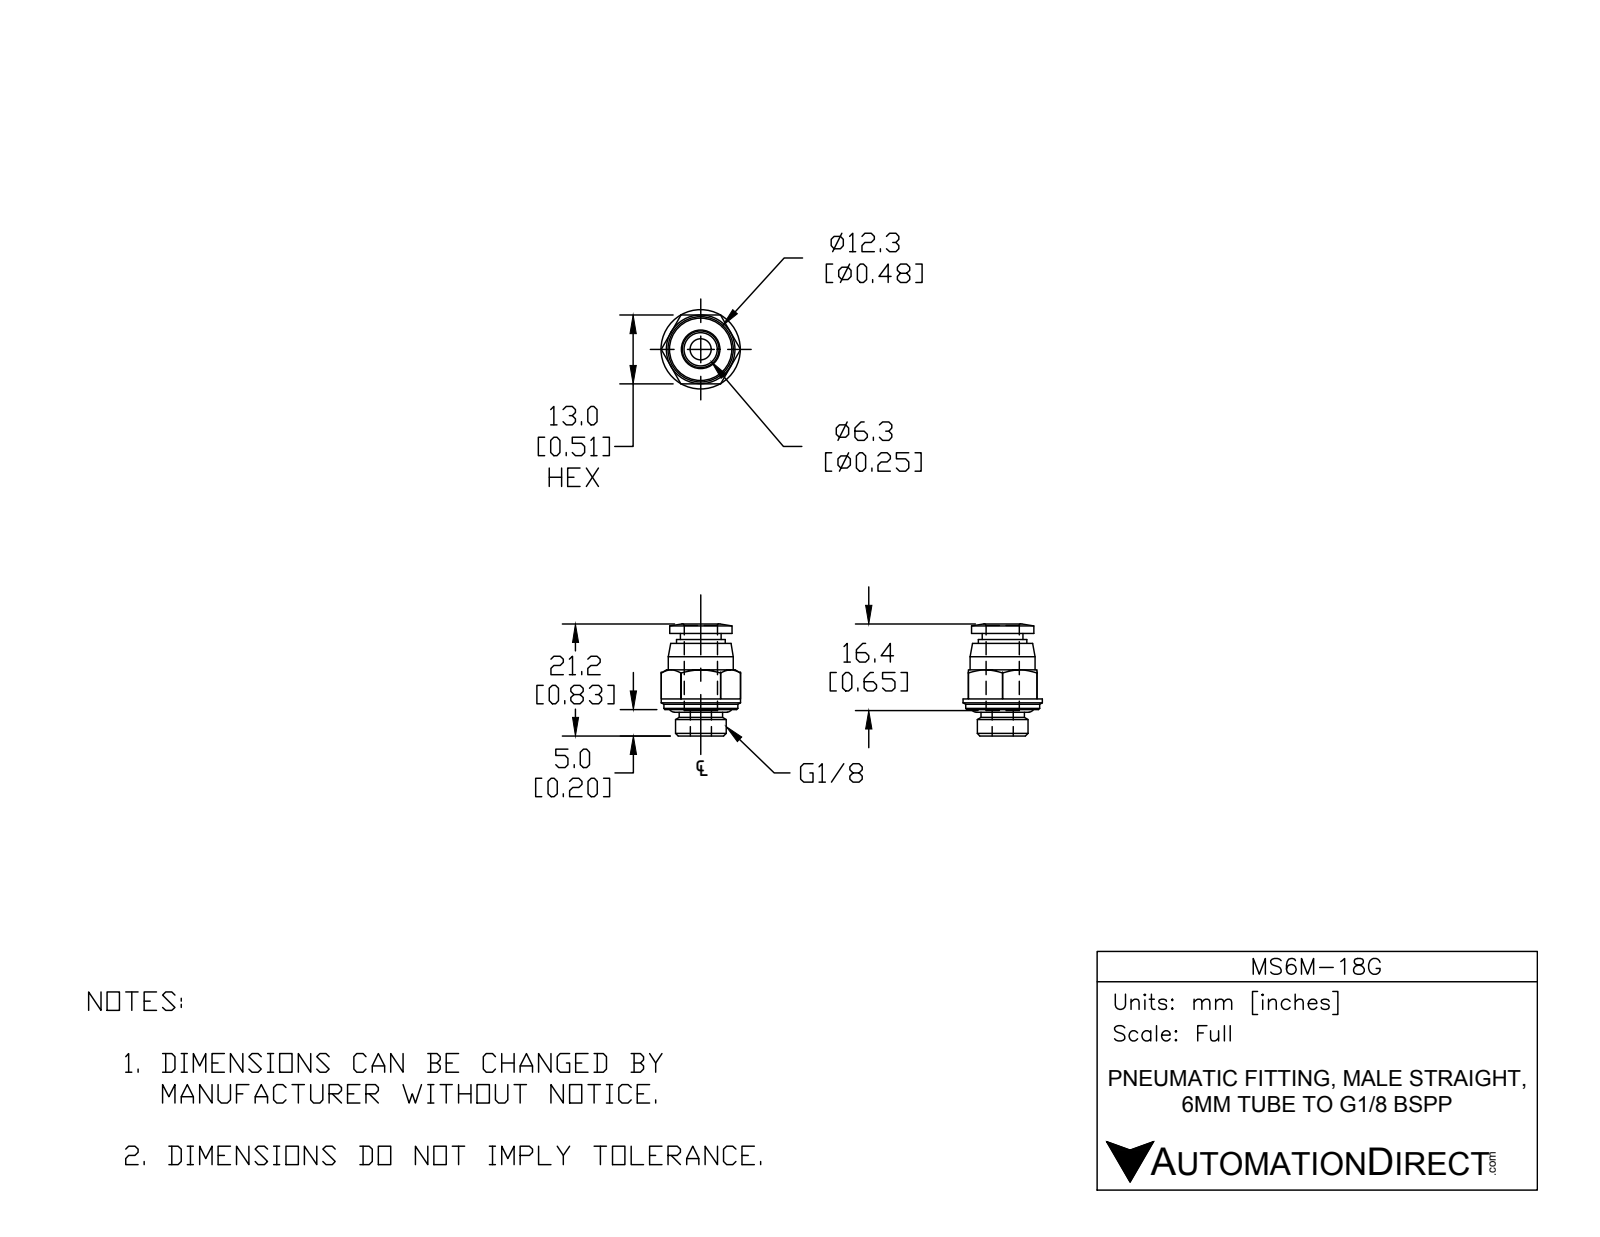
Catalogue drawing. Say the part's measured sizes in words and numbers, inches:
The part is named "MS6M-18G". Its 3-D file was written by "SolidWorks 2015 (AUTOMOTIVE_DESIGN)". It is 2 solids with 69 faces: 21 planar, 22 cylindrical and 26 other. Overall it measures 0.835 by 0.591 by 0.591 inches. Its volume is 0.107 cubic inches and its surface area 2.869 square inches. Round holes: 1 of diameter 0.157, 1 of diameter 0.248. Round bosses or shafts: 1 of diameter 0.591, 1 of diameter 0.551, 1 of diameter 0.484, 1 of diameter 0.465, 1 of diameter 0.378, 1 of diameter 0.362, 1 of diameter 0.323, 1 of diameter 0.303. The main face-to-face distances are 0.512, 0.252, 0.764, 0.689, 0.437, 0.075, 0.276, 0.024, 0.413, 0.488.
